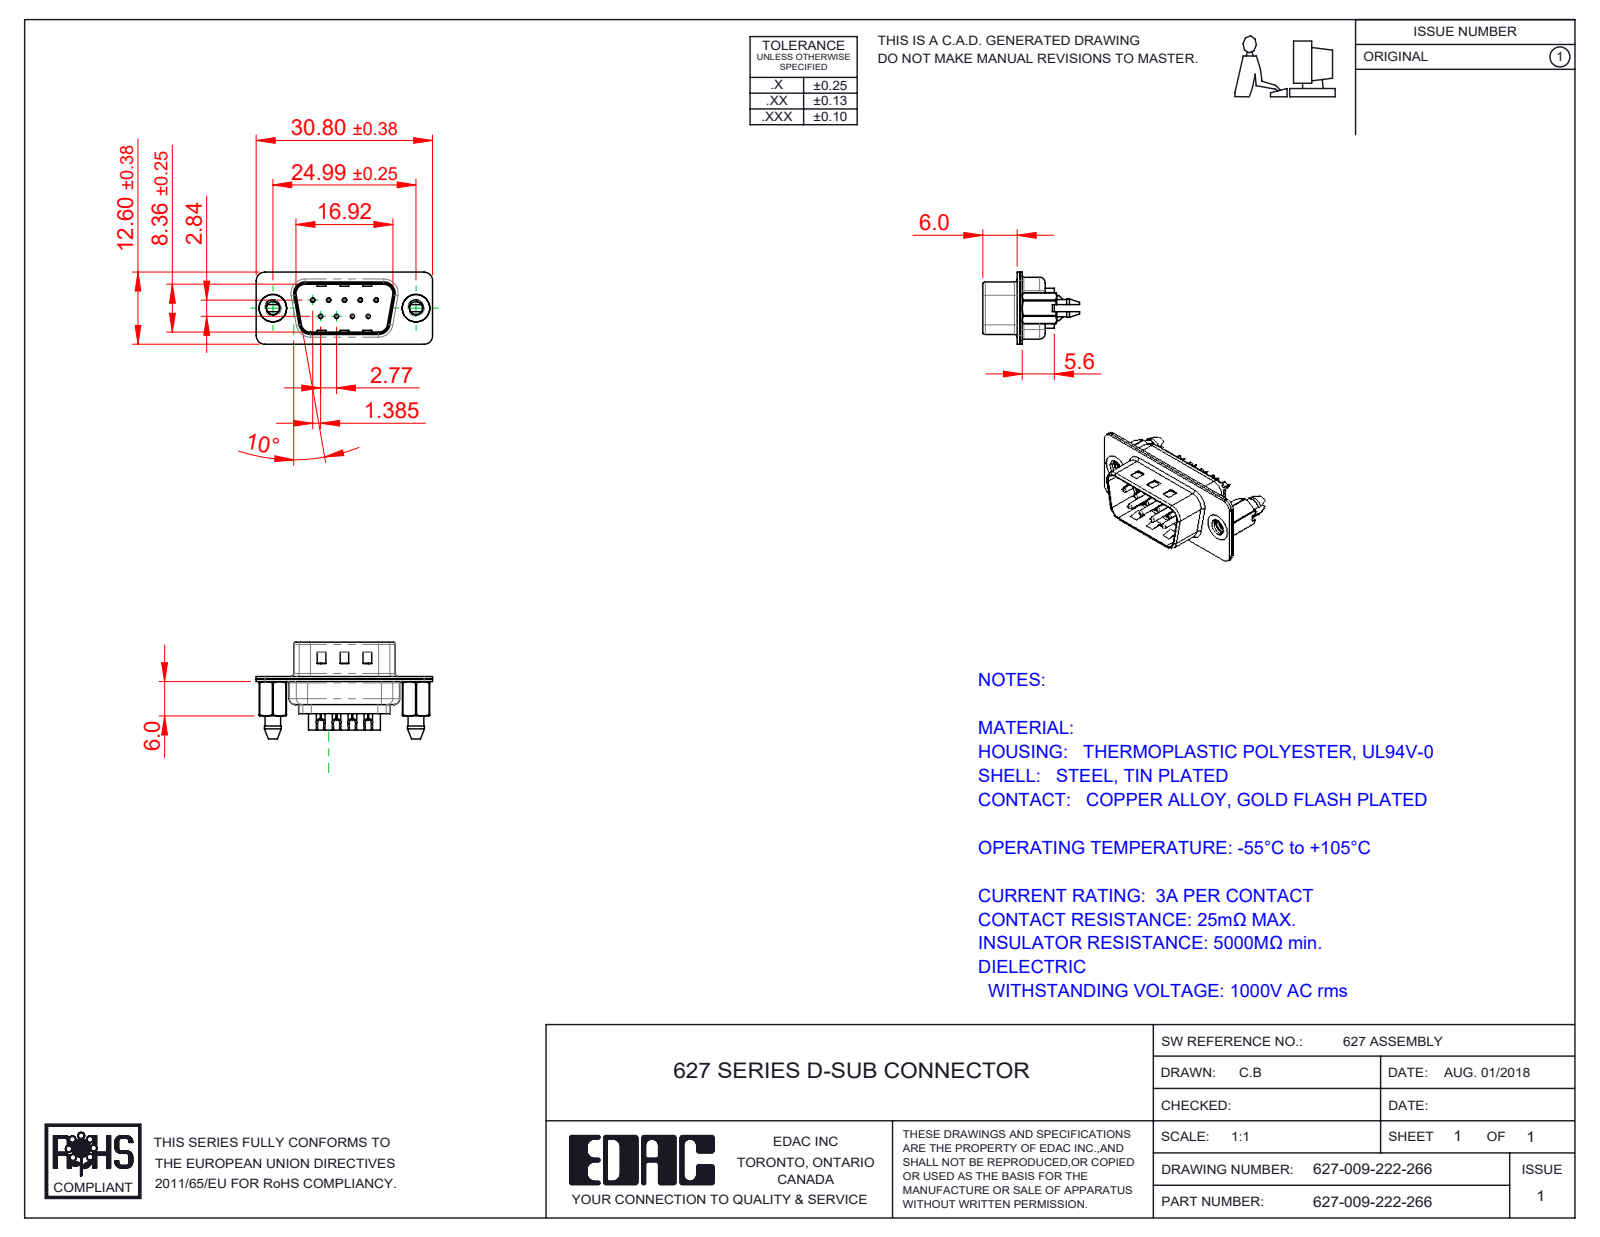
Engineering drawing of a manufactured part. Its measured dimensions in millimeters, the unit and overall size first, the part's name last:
Units: millimetres
Overall size (bounding box): 30.8 × 16.9 × 12.6
Round holes (diameter × count): ⌀0.35 ×9, ⌀1.1 ×9, ⌀1.6 ×9, ⌀2.26 ×2, ⌀4 ×2, ⌀4.8 ×2
Round bosses / shafts (diameter × count): ⌀2 ×9, ⌀1.5 ×9, ⌀0.75 ×9, ⌀4.9 ×2
Partial cylindrical surfaces — rounded edges, fillets, slot ends (radius × count): R1.5 ×20, R2 ×12, R1.6 ×10, R0.5 ×8, R1 ×6, R0.25 ×4, R0.6 ×4, R0.65 ×4
Main face-to-face distances: 0.45, 0.4, 0.9, 0.82, 9.58, 1.4, 8.76, 6.5, 0.5, 1.5
Hole centre spacings: 3.16, 2.77, 5.54, 5.03, 5.04, 8.31, 7.48, 7.49
Volume: 1 430 mm³ · Surface area: 4 244 mm²
Bodies: 14 solids, 954 faces (265 planar, 422 cylindrical, 267 other)
Part name (STEP PRODUCT): 627 Contact Row 1_22L; 627 Housing_09 LP; 627 Contact Row 2_22L; 627 4-40 Threaded Boardlock_LP (+3 more)
STEP written by: SolidWorks 2020 (CONFIG_CONTROL_DESIGN)
